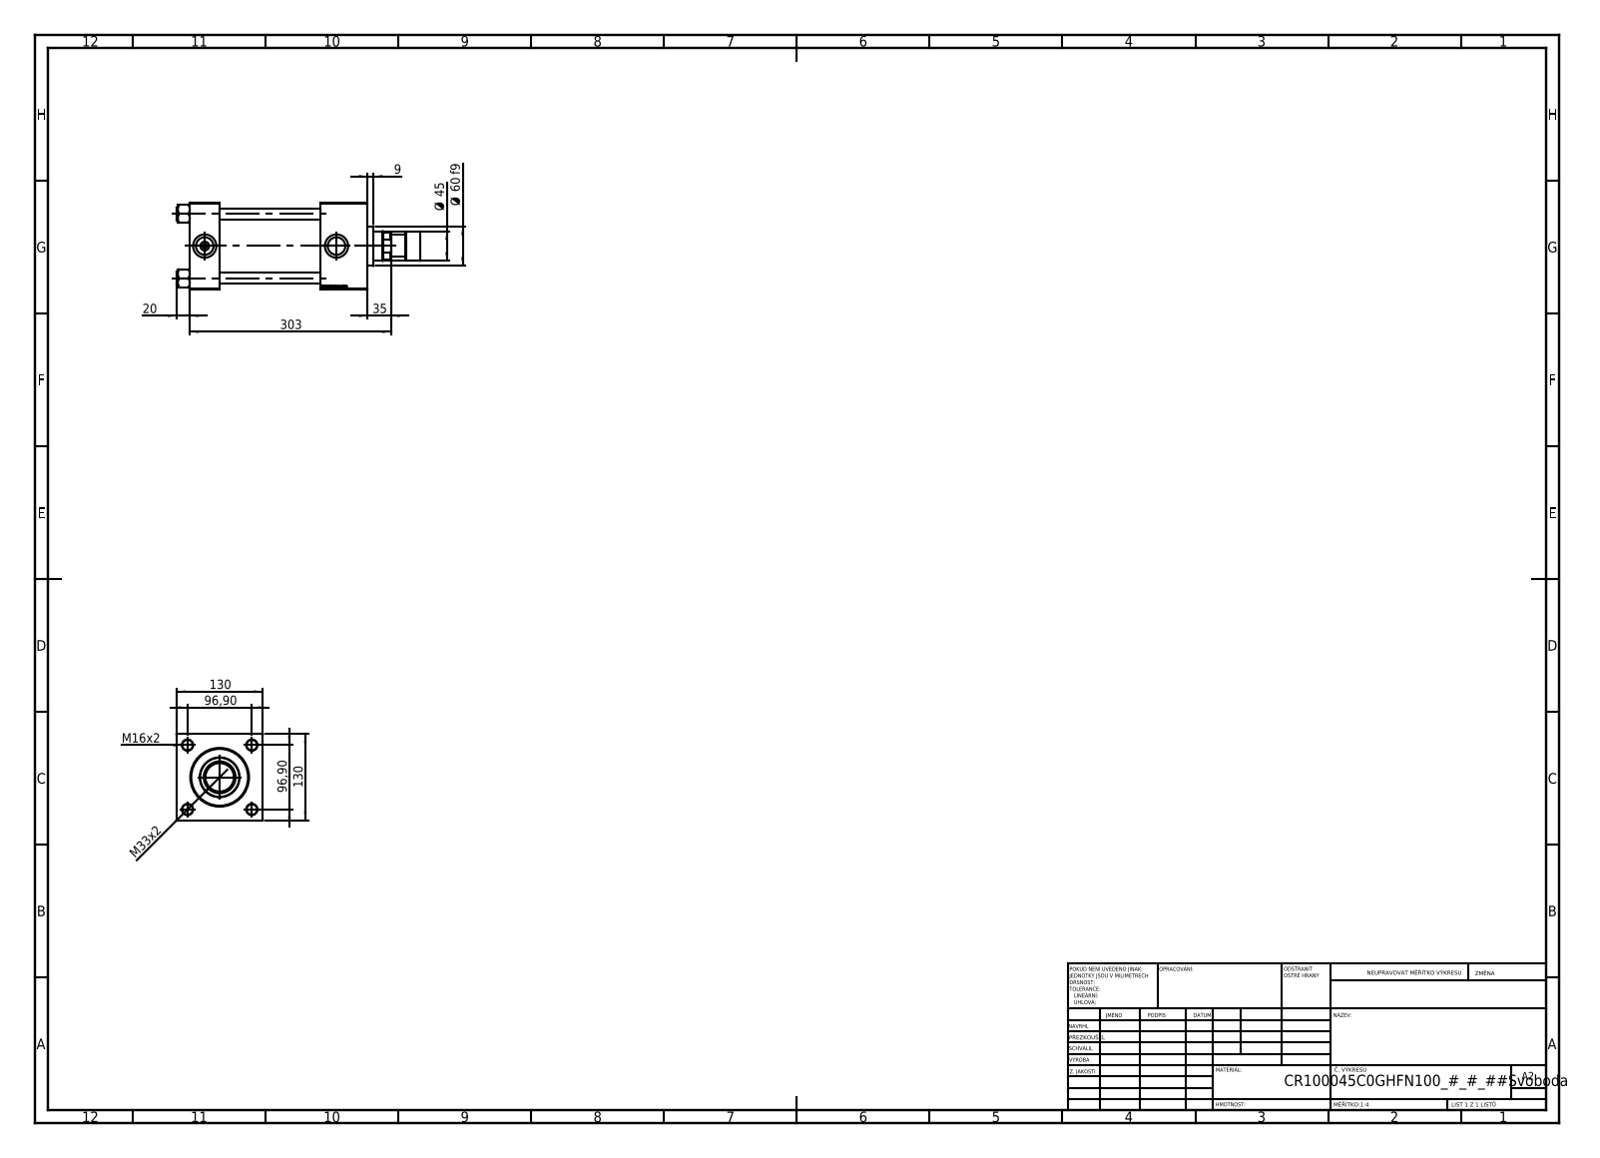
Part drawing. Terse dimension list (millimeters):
name: V215_VC_A; NUT_M5_C; V215CR_C_Body; V215CR_C_TYCINKA (+2 more)
written by: SolidWorks 2019 (CONFIG_CONTROL_DESIGN)
unit: mm
bodies: 12 solids, 1209 faces (577 planar, 90 cylindrical, 542 other)
size: 367 × 130 × 130
volume: 2 747 000 mm³; area: 413 934 mm²
holes: 4× ⌀16, 2× ⌀7, 2× ⌀26.44, 2× ⌀35, 1× ⌀31.5, 1× ⌀45, 1× ⌀48, 1× ⌀76, 1× ⌀85.5, 1× ⌀100
bosses: 4× ⌀19, 1× ⌀106, 1× ⌀60, 1× ⌀44, 1× ⌀33
face distances: 130, 45, 268, 223, 151, 196, 72, 96, 51, 100
hole spacings: 68.52, 96.9, 137.04, 198.5
